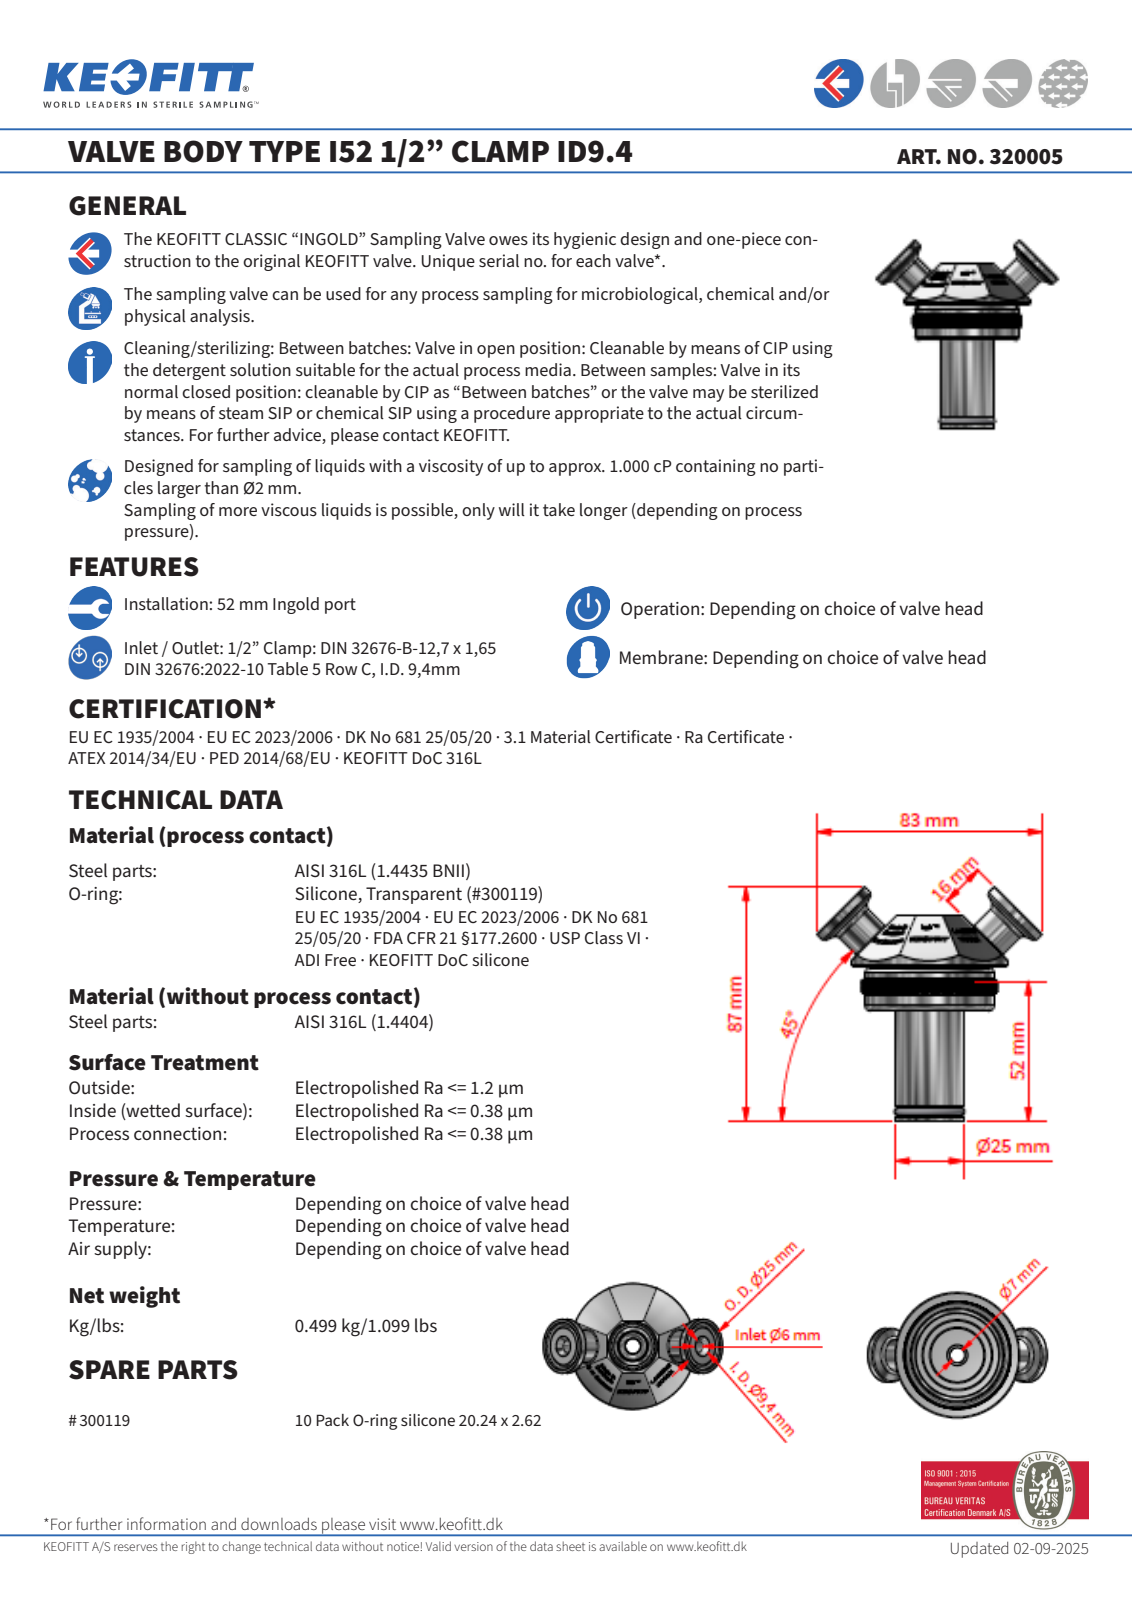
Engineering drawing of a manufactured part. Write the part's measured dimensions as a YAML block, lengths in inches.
part_name: "320005"
step_written_by: "Autodesk Inventor 2022 (AUTOMOTIVE_DESIGN)"
units: inches
bodies: {solids: 2, faces: 50, planar: 17, cylindrical: 13, other: 20}
overall_size: [3.426, 3.281, 2.283]
volume: 5.451
surface_area: 27.07
round_bosses_or_shafts:
  - {diameter: 0.984, count: 3}
  - {diameter: 0.591, count: 2}
  - {diameter: 2.283, count: 1}
  - {diameter: 1.969, count: 1}
  - {diameter: 1.89, count: 1}
  - {diameter: 1.417, count: 1}
  - {diameter: 0.819, count: 1}
face_to_face_distances: [0.686, 0.63, 0.056, 1.578, 2.208, 2.264, 3.012, 1.434, 0.804, 0.748]
